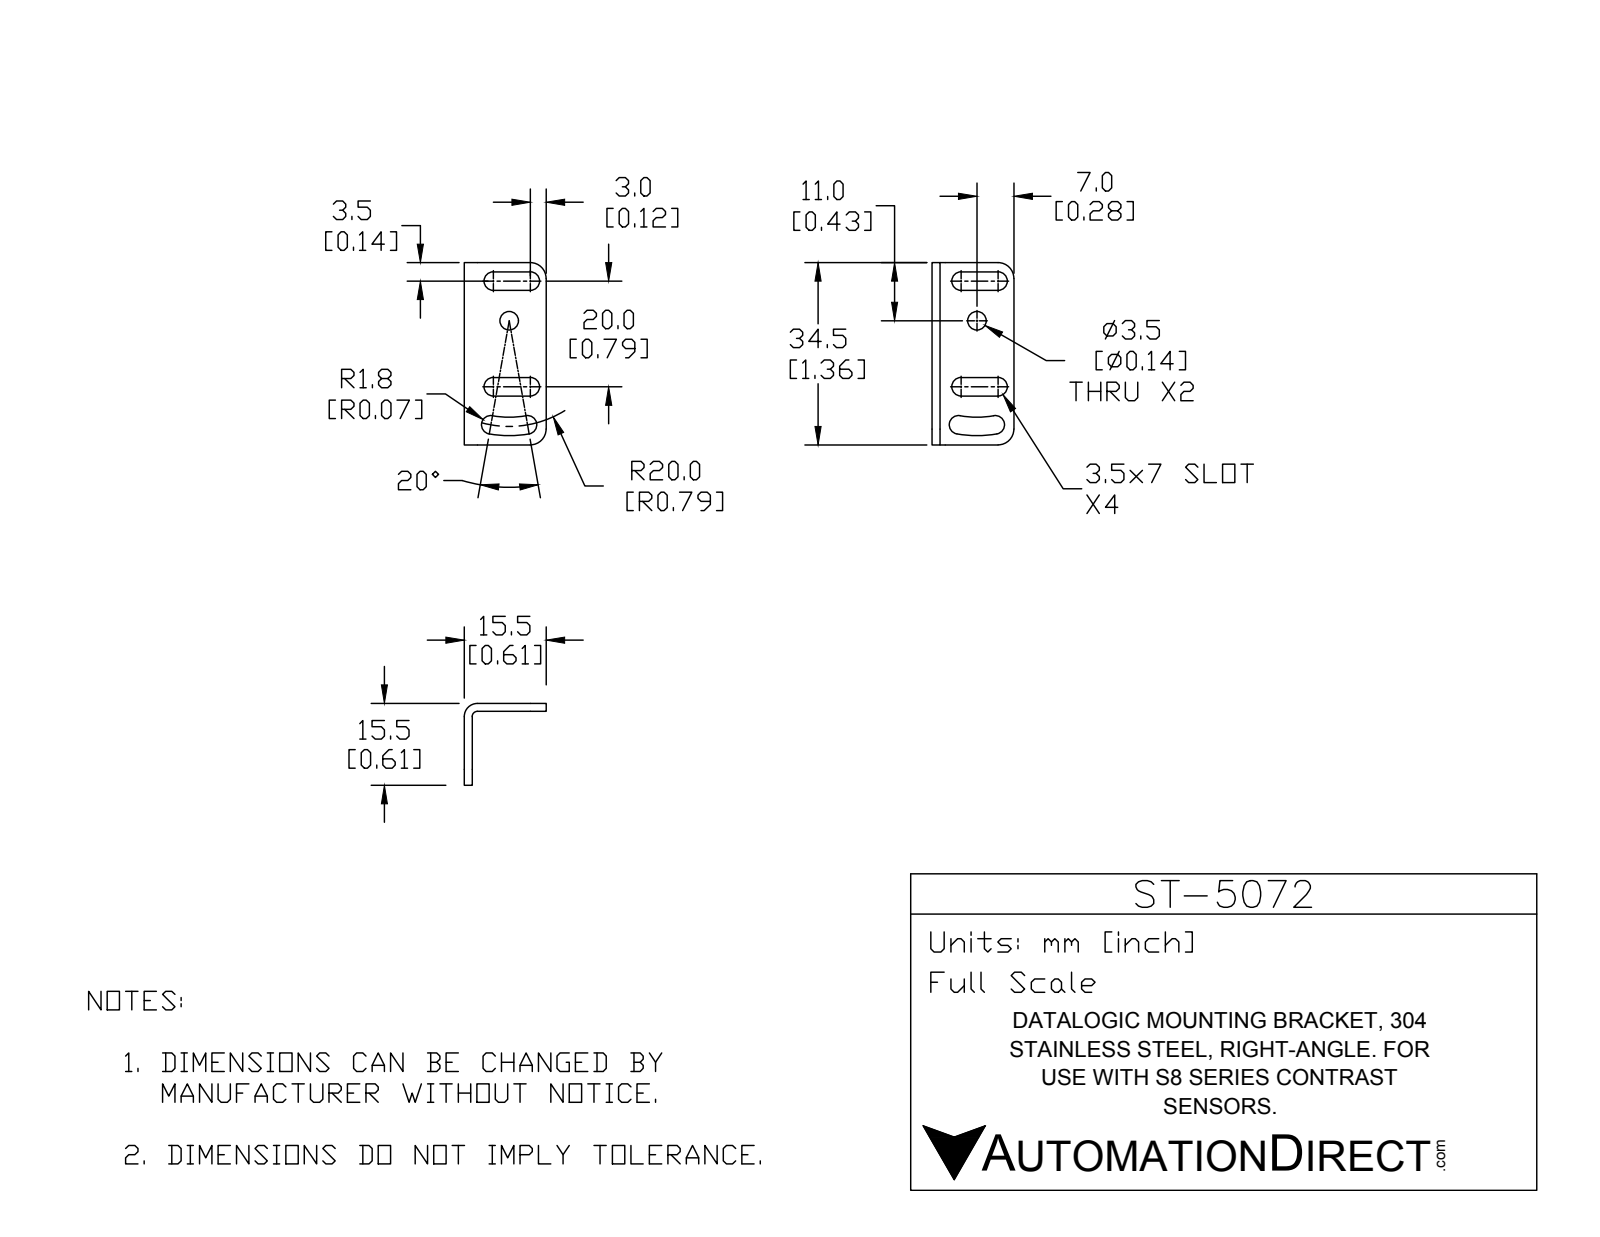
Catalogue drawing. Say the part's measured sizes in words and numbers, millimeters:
The part is named "ST-5072". Its 3-D file was written by "SolidWorks 2016 (AUTOMOTIVE_DESIGN)". It is 1 solid with 48 faces: 16 planar, 32 cylindrical and 0 other. Overall it measures 34.5 by 15.5 by 15.5 millimeters. Its volume is 1 140 cubic millimeters and its surface area 1 960 square millimeters. Round holes: 2 of diameter 3.5. Partial cylindrical surfaces (rounded edges, fillets, slot ends): 12 of radius 1.75, 4 of radius 3, 2 of radius 18.25, 2 of radius 21.75, 1 of radius 1, 1 of radius 2.5. The main face-to-face distances are 1.5, 15.5, 14, 3.5, 20, 34.5, 1.75, 32.75, 21.75, 25.25.
